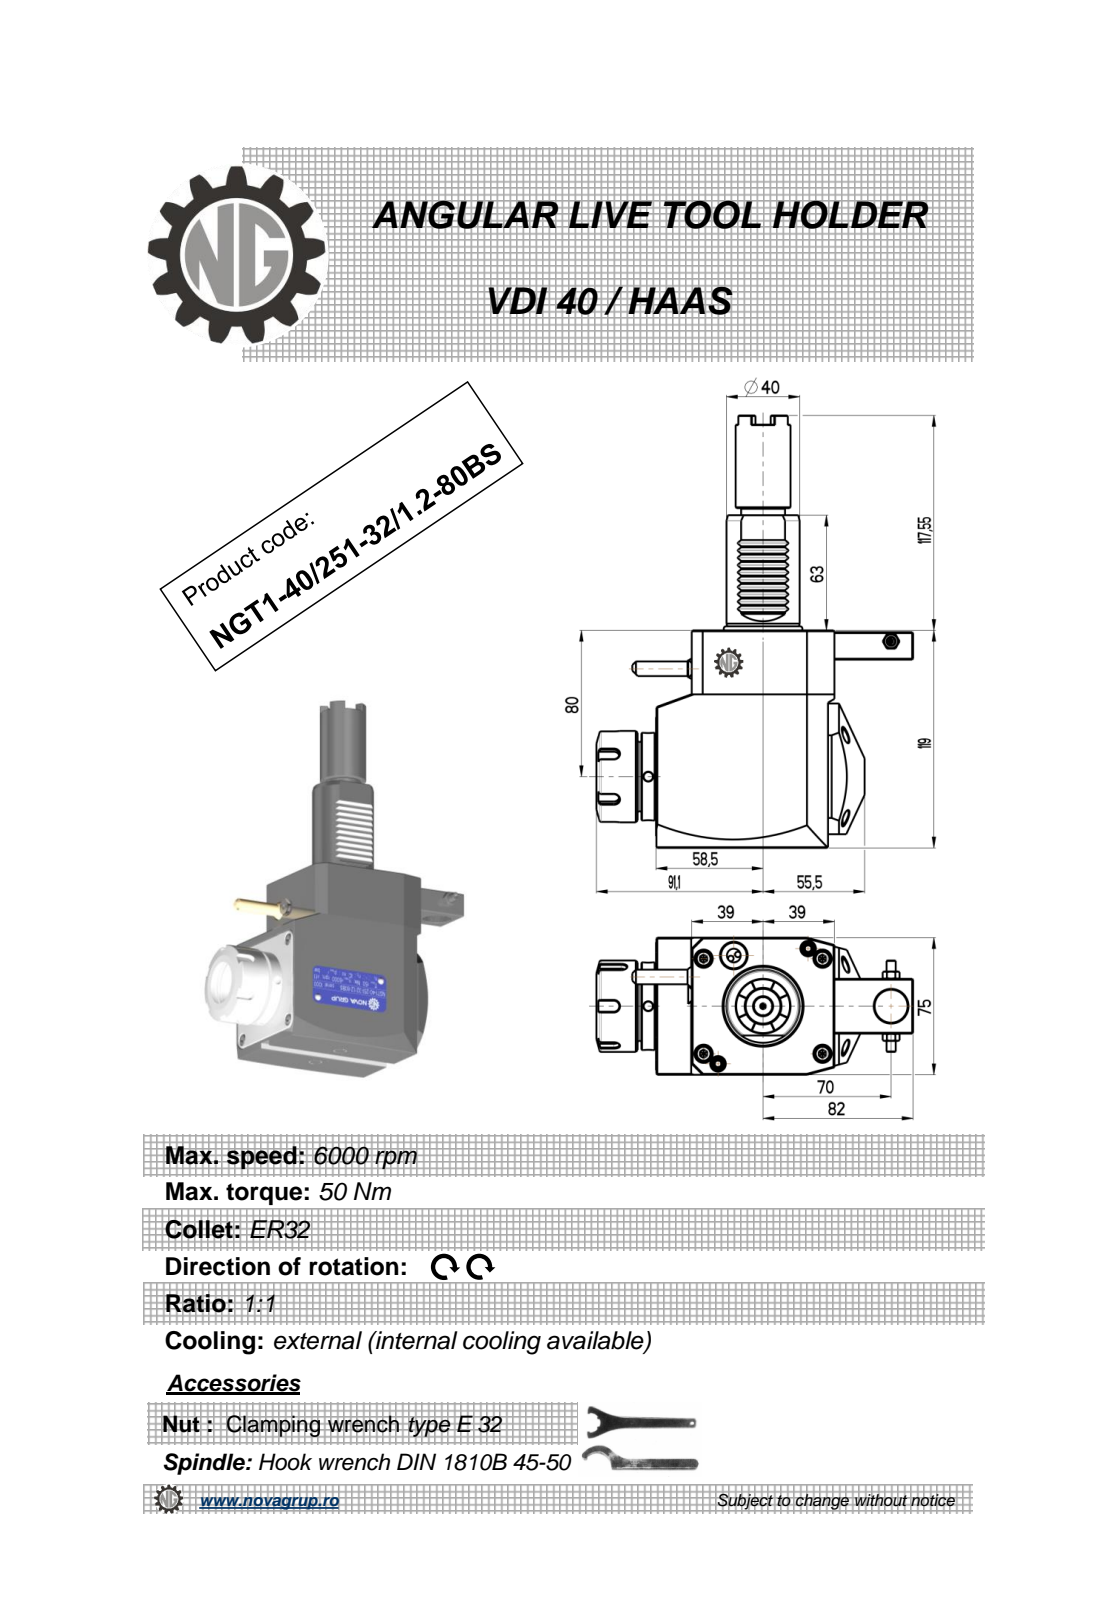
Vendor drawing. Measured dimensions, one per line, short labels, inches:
name: NGT1_40_251_32_1_2_80BS
written by: PRO/ENGINEER BY PARAMETRIC TECHNOLOGY CORPORATION, 2010280 (CONFIG_CONTROL_DESIGN)
unit: in
bodies: 1 solid, 475 faces (236 planar, 100 cylindrical, 139 other)
size: 9.313 × 6.815 × 3.016
volume: 62.12 in³; area: 128 in²
holes: 3× ⌀0.197, 1× ⌀0.118, 1× ⌀0.165, 1× ⌀0.374, 1× ⌀0.709, 1× ⌀1.063
bosses: 1× ⌀1.969, 1× ⌀1.89, 1× ⌀1.634, 1× ⌀1.614, 1× ⌀1.575, 1× ⌀1.181, 1× ⌀0.945, 1× ⌀0.394
rounds: 12× R0.01, 10× R0.012, 6× R0.008, 5× R0.118, 2× R0.228, 2× R0.236, 2× R23.622, 1× R0.02
face distances: 2.953, 4.685, 0.768, 3.839, 3.071, 0.039, 0.886, 0.138, 0.787, 4.488
hole spacings: 0.824, 2.407, 2.854, 5.226, 5.983
